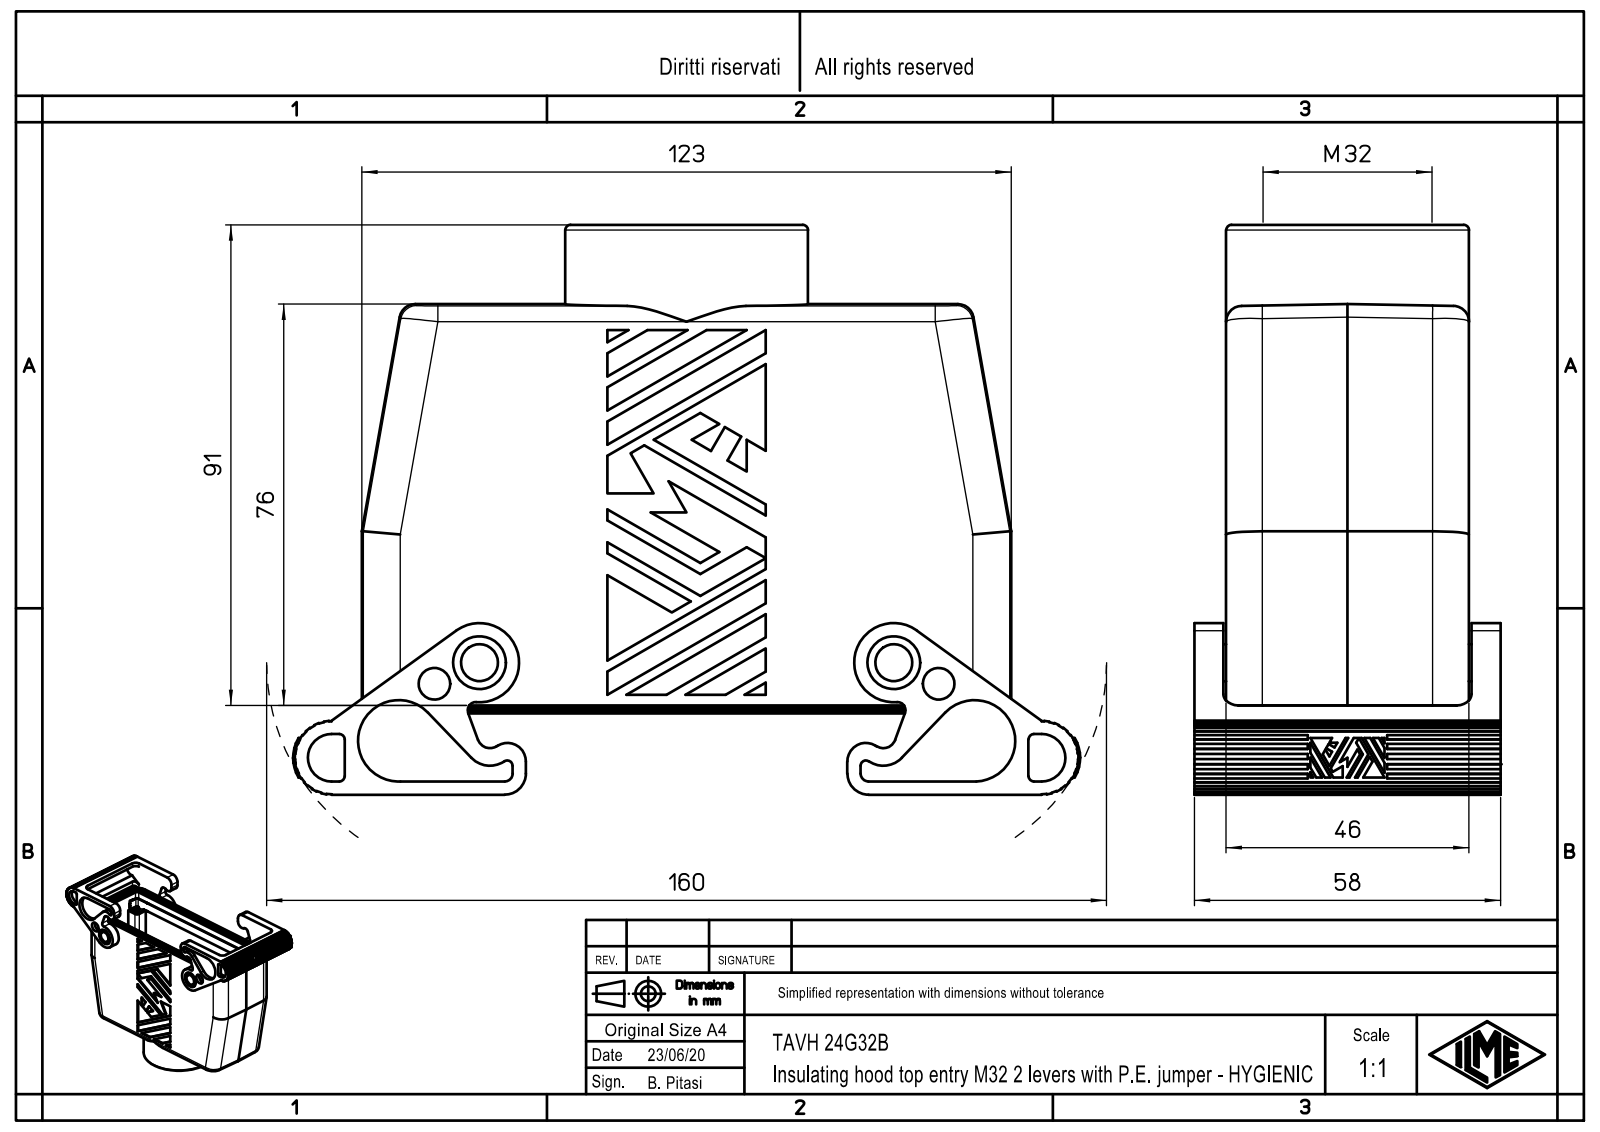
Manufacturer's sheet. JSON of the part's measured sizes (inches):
{"part_name": "TAVH_24G32B", "step_written_by": "Creo Elements/Direct Modeling 20.1B 02-Apr-2019 (C) Parametric Technology GmbH (AUTOMOTIVE_DESIGN)", "units": "inches", "bodies": {"solids": 1, "faces": 799, "planar": 533, "cylindrical": 238, "other": 28}, "overall_size": [5.87, 4.248, 2.283], "volume_in3": 11.43, "surface_area_in2": 123.6, "round_holes": [[0.138, 4], [0.202, 4], [0.256, 4], [0.236, 2], [0.394, 2], [1.102, 1], [1.26, 1]], "round_bosses_or_shafts": [[0.276, 2], [1.811, 1]], "partial_cylinders_radius": [[0.059, 16], [0.118, 10], [0.276, 10], [0.039, 8], [0.071, 8], [0.079, 8], [0.051, 4], [0.063, 4]], "face_to_face_distances": [1.811, 0.02, 1.831, 0.039, 1.791, 0.098, 0.217, 0.236, 0.256, 2.028], "hole_center_spacings": [2.115, 0.37, 1.063, 3.429, 4.094, 4.23, 3.091, 3.76]}
